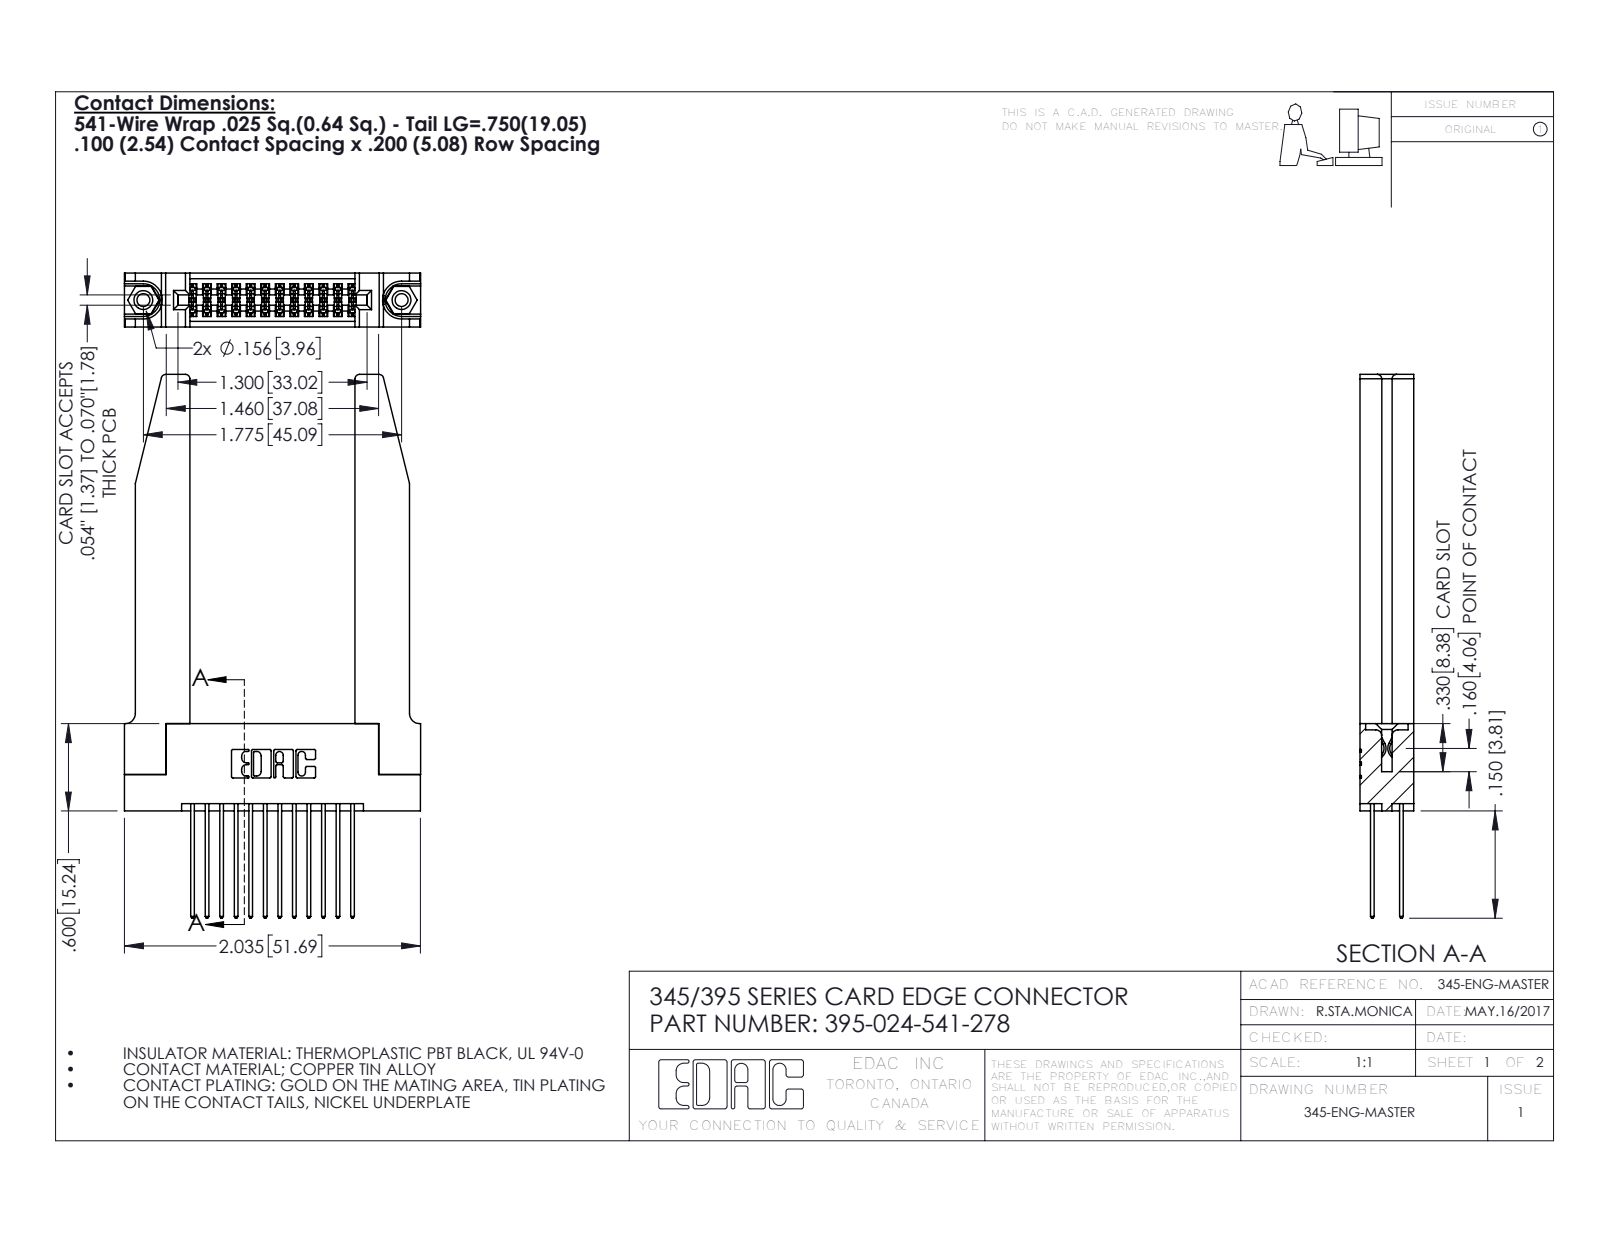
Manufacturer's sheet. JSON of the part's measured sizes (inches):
{"part_name": "345-250-001_345-250-001-102; 395-024-541-278; 345-292-001_345-293-141; 345 Part_Flush Mounting Lugs - 0.156 Dia-TH (+1 more)", "step_written_by": "SolidWorks 2016 (CONFIG_CONTROL_DESIGN)", "units": "inches", "bodies": {"solids": 29, "faces": 1560, "planar": 1014, "cylindrical": 494, "other": 52}, "overall_size": [3.737, 2.036, 0.37], "volume_in3": 0.772, "surface_area_in2": 21.89, "round_holes": [[0.089, 2], [0.125, 2], [0.156, 2], [0.064, 1]], "round_bosses_or_shafts": [[0.155, 2]], "partial_cylinders_radius": [[0.006, 36], [0.01, 24], [0.01, 22], [0.03, 8], [0.007, 6], [0.031, 6], [0.026, 3], [0.014, 2]], "face_to_face_distances": [0.37, 0.072, 0.298, 0.2, 0.098, 0.272, 0.025, 0.15, 0.148, 0.225], "hole_center_spacings": [0.27, 1.543, 1.775]}
